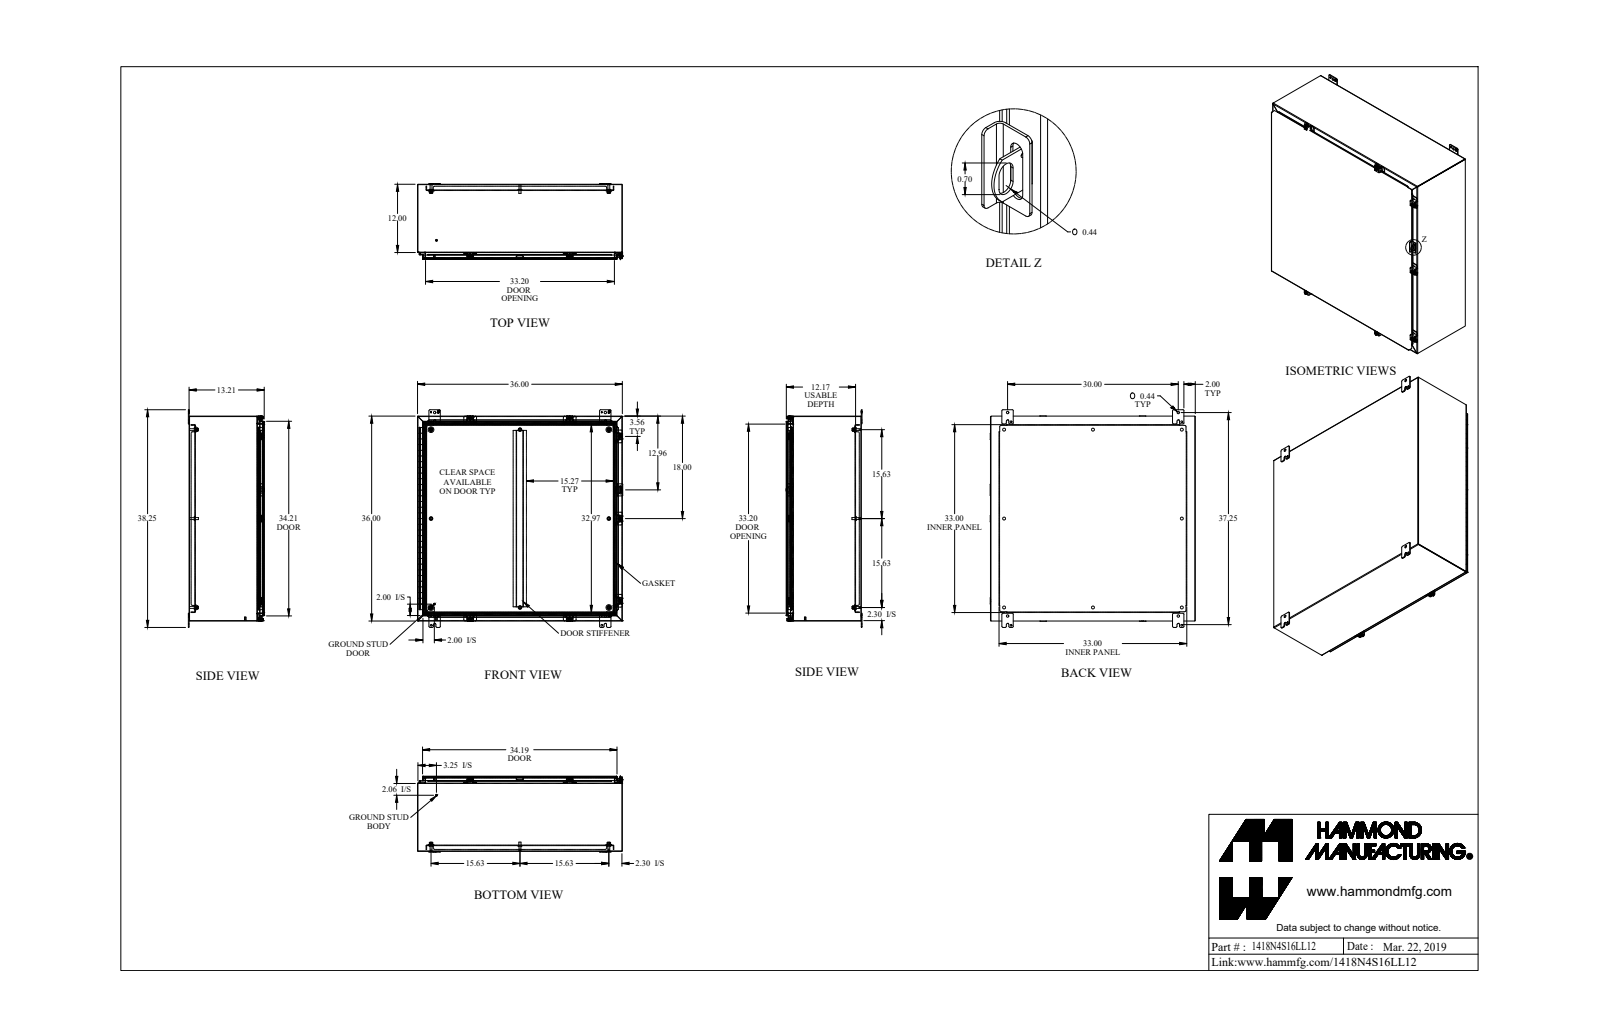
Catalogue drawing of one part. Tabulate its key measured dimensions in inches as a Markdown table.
| quantity | value |
| --- | --- |
| part name | 1418N4S16LL12_Default |
| STEP written by | SolidWorks 2019 (CONFIG_CONTROL_DESIGN) |
| units | inches |
| bodies | 62 solids, 1983 faces (1036 planar, 751 cylindrical, 196 other) |
| overall size | 38.25 × 36.063 × 13.375 |
| volume | 475.1 in³ |
| surface area | 12 448 in² |
| round holes (diameter × count) | 0.5 × 8, 0.213 × 7, 0.265 × 7, 0.375 × 7, 0.307 × 4, 0.313 × 4, 0.437 × 4, 0.445 × 4, 0.11 × 1, 0.125 × 1 |
| round bosses / shafts (diameter × count) | 0.65 × 8, 0.375 × 8, 0.332 × 8, 0.5 × 7, 0.39 × 7, 0.244 × 7, 1 × 4, 0.313 × 2 |
| partial cylindrical surfaces (radius × count) | 0.25 × 40, 0.048 × 33, 0.143 × 33, 0.188 × 30, 0.036 × 22, 0.108 × 22, 0.125 × 14, 0.141 × 14 |
| main face-to-face distances | 0.072, 35.928, 13.066, 13.138, 0.072, 13.138, 0.095, 13.21, 0.937, 1.009 |
| hole center spacings | 15.625, 31.25, 34.939, 34.939, 7.196, 9.004, 15.625, 19.035 |
